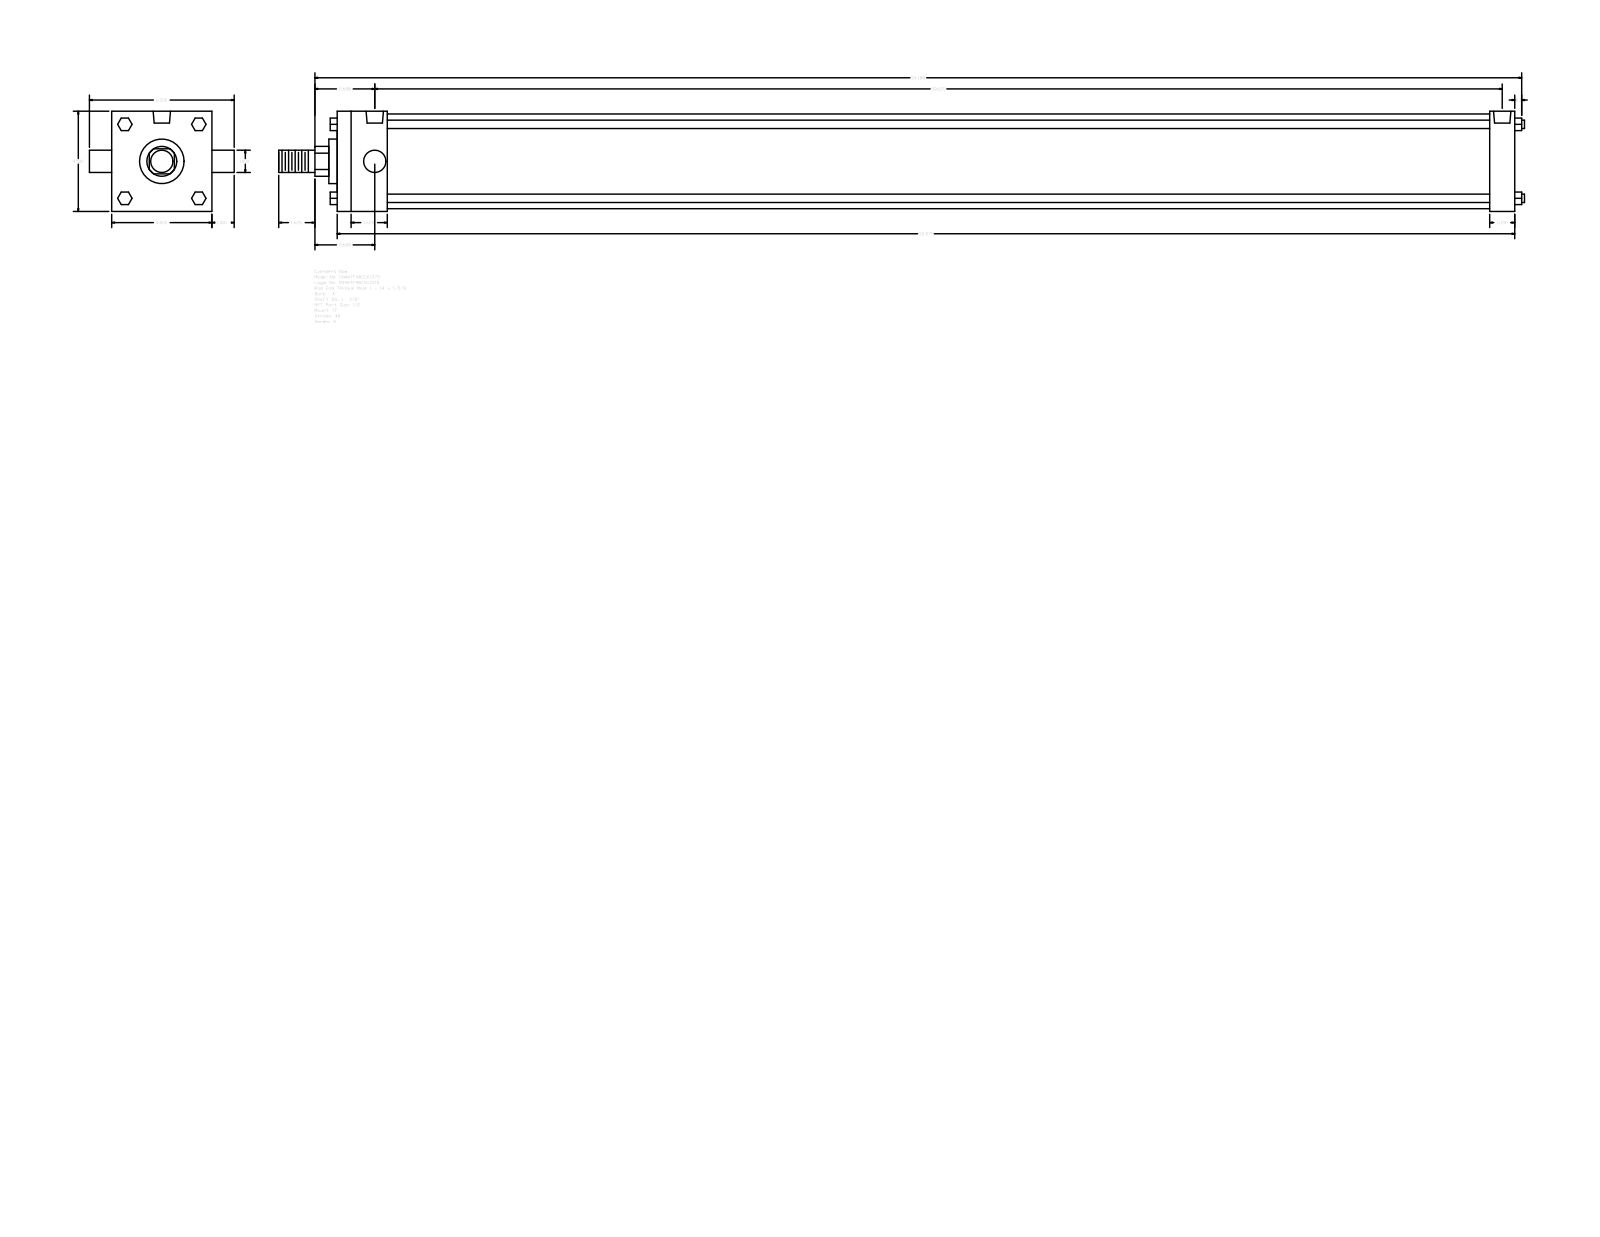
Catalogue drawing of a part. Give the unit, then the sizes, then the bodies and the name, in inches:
Units: inches
Overall size (bounding box): 55.937 × 6.5 × 4.5
Round holes (diameter × count): ⌀0.344 ×3, ⌀0.778 ×2
Round bosses / shafts (diameter × count): ⌀0.375 ×4, ⌀1 ×2, ⌀4.25 ×1, ⌀2 ×1, ⌀1.375 ×1
Partial cylindrical surfaces — rounded edges, fillets, slot ends (radius × count): R0.672 ×1
Main face-to-face distances: 4.5, 52.875, 2.25, 51.75, 1.125, 49.5, 50.625, 2.625, 0.563, 1
Hole centre spacings: 0.125, 50.5, 50.375, 50.625
Bodies: 0 solids, 120 faces (92 planar, 28 cylindrical, 0 other)
Part name (STEP PRODUCT): A_TF__0400_1.375
STEP written by: GSSL Pune (CONFIG_CONTROL_DESIGN)
